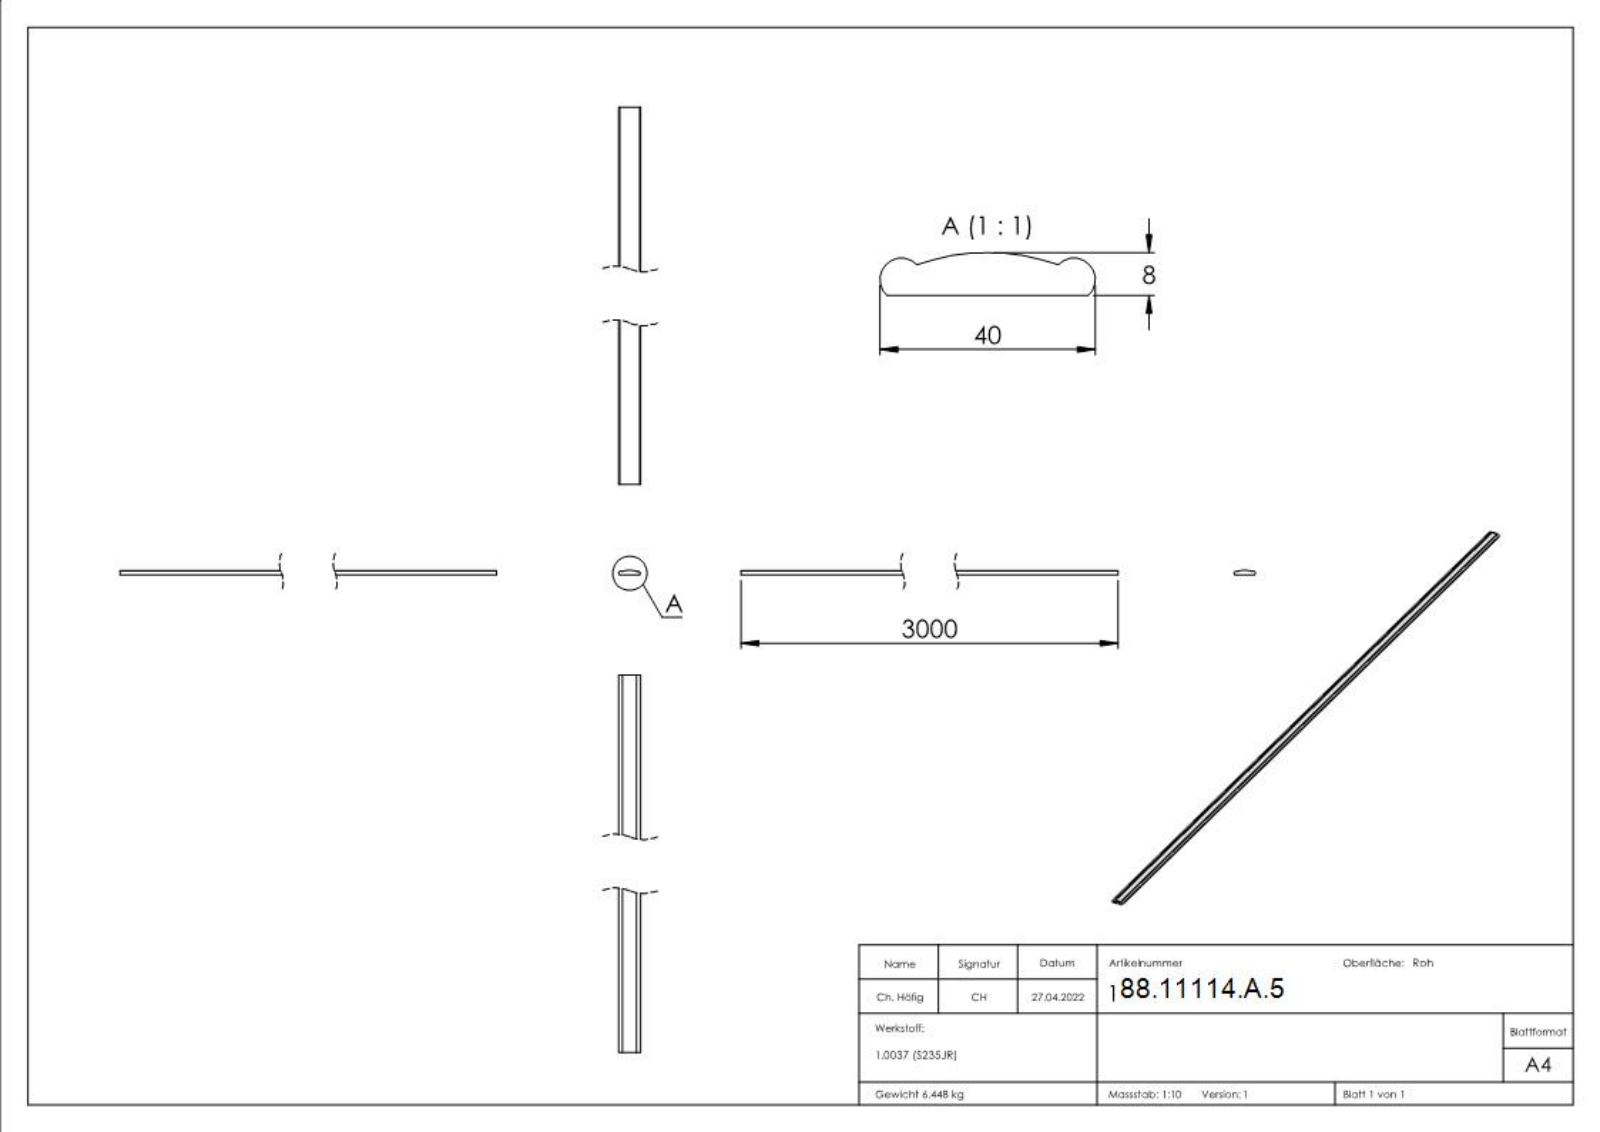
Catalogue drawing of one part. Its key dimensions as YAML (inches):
part_name: "114-A-5"
step_written_by: "SolidWorks 2018 (CONFIG_CONTROL_DESIGN)"
units: inches
bodies: {solids: 1, faces: 229, planar: 150, cylindrical: 3, other: 76}
overall_size: [118.11, 1.575, 0.315]
volume: 50.45
surface_area: 418.4
partial_cylinders:
  - {radius: 0.157, count: 2}
  - {radius: 1.575, count: 1}
face_to_face_distances: [118.11, 0.029, 0.074, 0.04, 0.02, 0.151, 0.156, 0.087, 0.055, 0.095]
